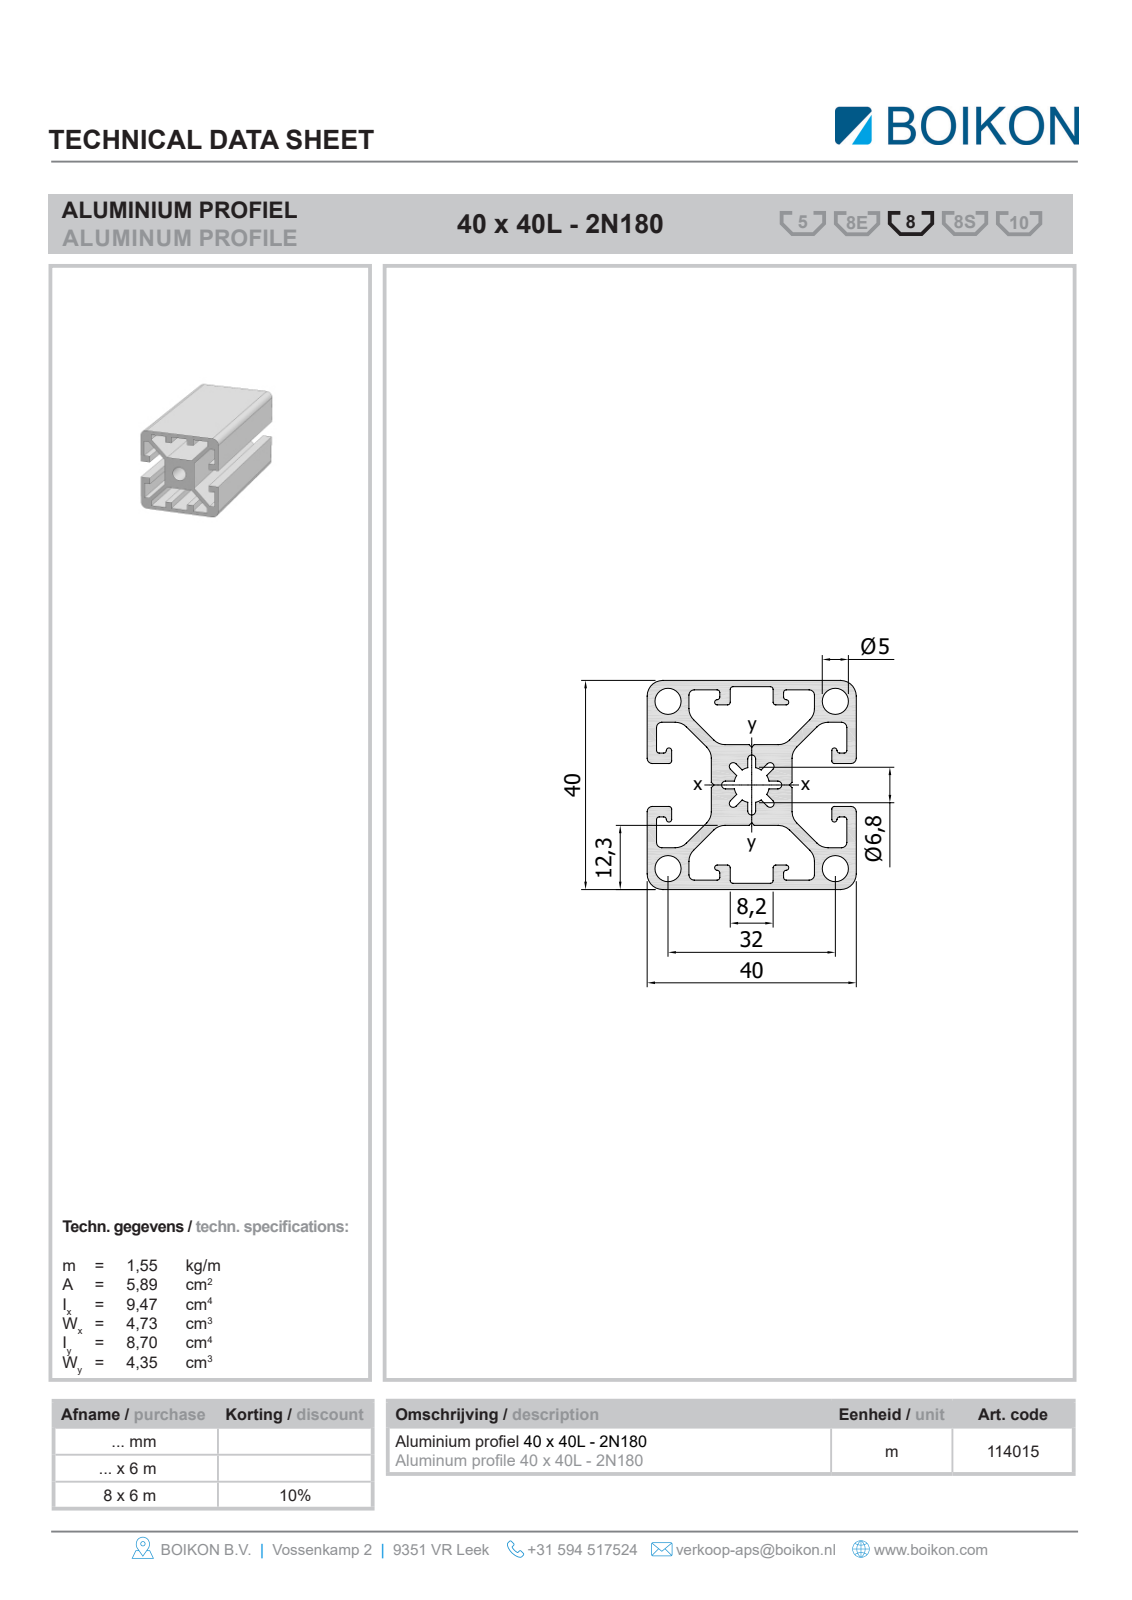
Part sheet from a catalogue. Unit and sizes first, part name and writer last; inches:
Units: inches
Overall size (bounding box): 39.37 × 1.575 × 1.575
Round holes (diameter × count): ⌀0.268 ×1
Partial cylindrical surfaces — rounded edges, fillets, slot ends (radius × count): R0.118 ×4
Main face-to-face distances: 0.071, 1.504, 1.575, 0.488, 1.087, 0.417, 1.016, 0.441, 0.323, 1.433
Volume: 38.67 in³ · Surface area: 739 in²
Bodies: 1 solid, 67 faces (62 planar, 5 cylindrical, 0 other)
Part name (STEP PRODUCT): Root; 11401540x40L-2N180BOIKON0
STEP written by: HiCAD 2013 1802.4 Build 509 (AUTOMOTIVE_DESIGN)
